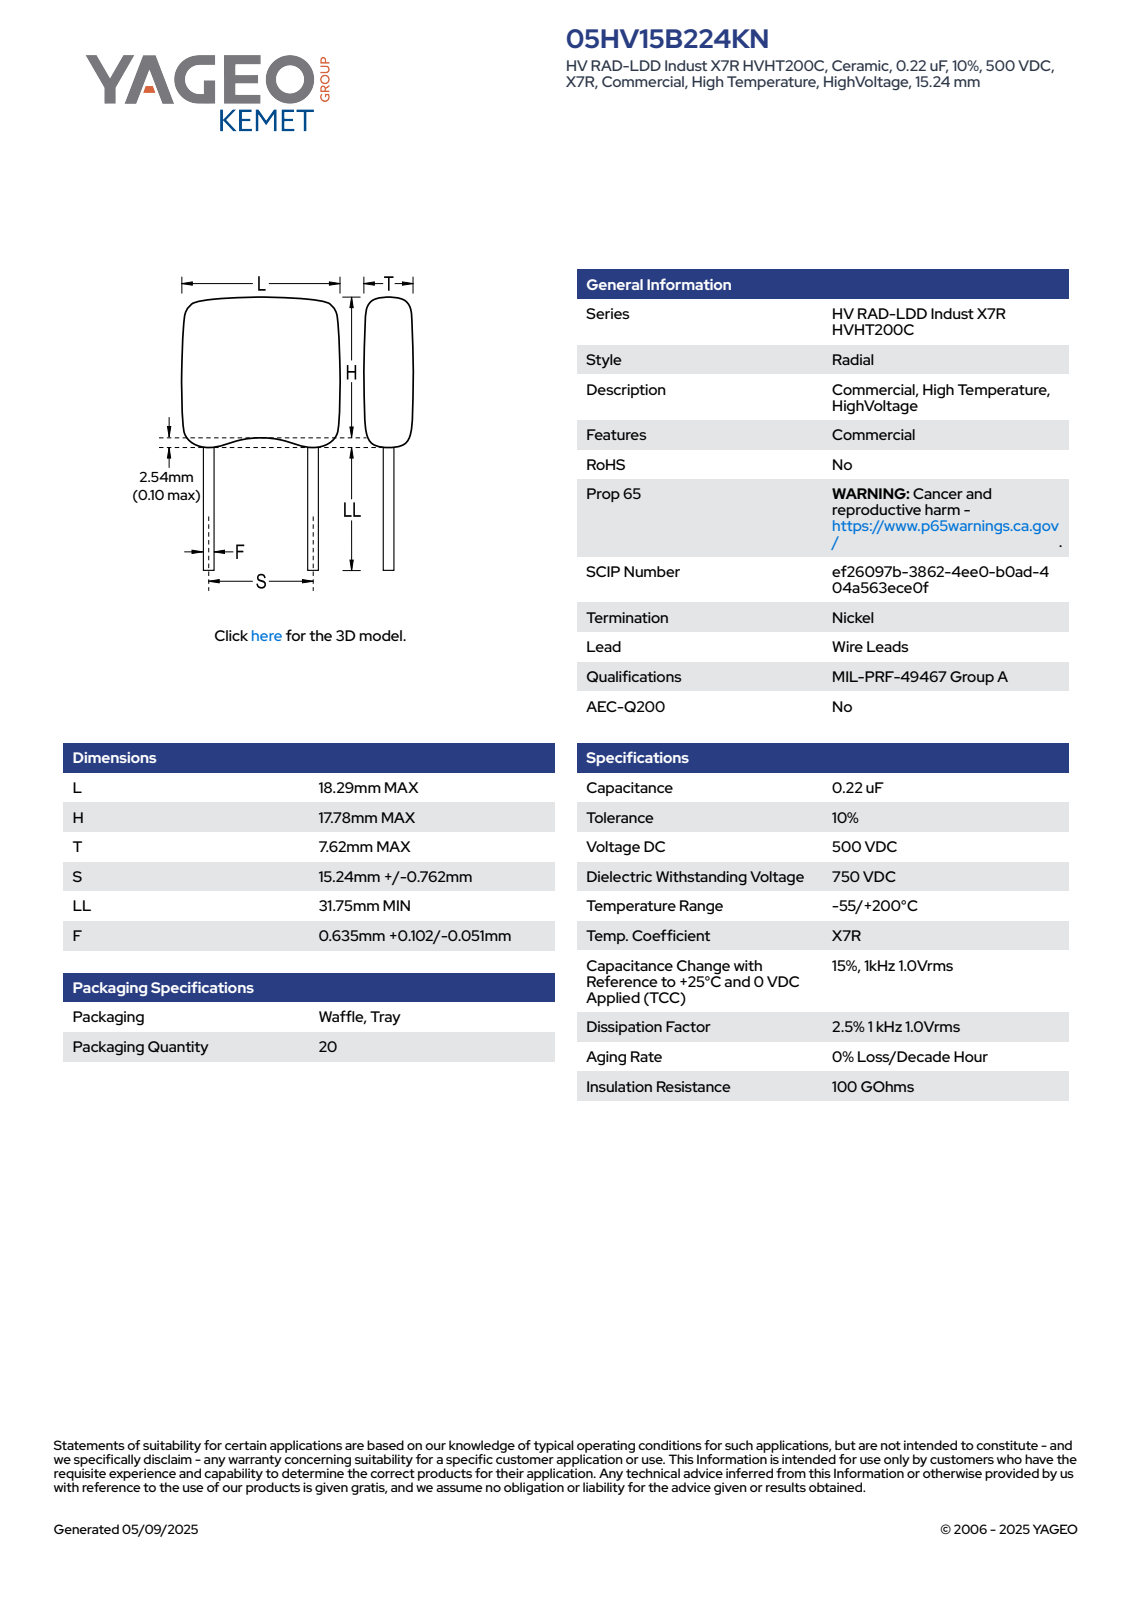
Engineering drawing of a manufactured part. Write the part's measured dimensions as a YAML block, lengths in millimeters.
part_name: "CCRM_RCST_HV15_L18.29H17.78T7.62S15.24LL31.75F0.737"
step_written_by: "SolidWorks 2021 (AUTOMOTIVE_DESIGN)"
units: millimeters
bodies: {solids: 4, faces: 94, planar: 66, cylindrical: 18, other: 10}
overall_size: [22.54, 18.29, 7.62]
volume: 2538
surface_area: 1237
round_bosses_or_shafts:
  - {diameter: 0.74, count: 2}
partial_cylinders:
  - {radius: 1, count: 8}
  - {radius: 0.5, count: 4}
face_to_face_distances: [7.62, 18.29, 19.36, 3.17, 22.53, 14.07, 10.9, 8.46, 11.75, 8.58]
